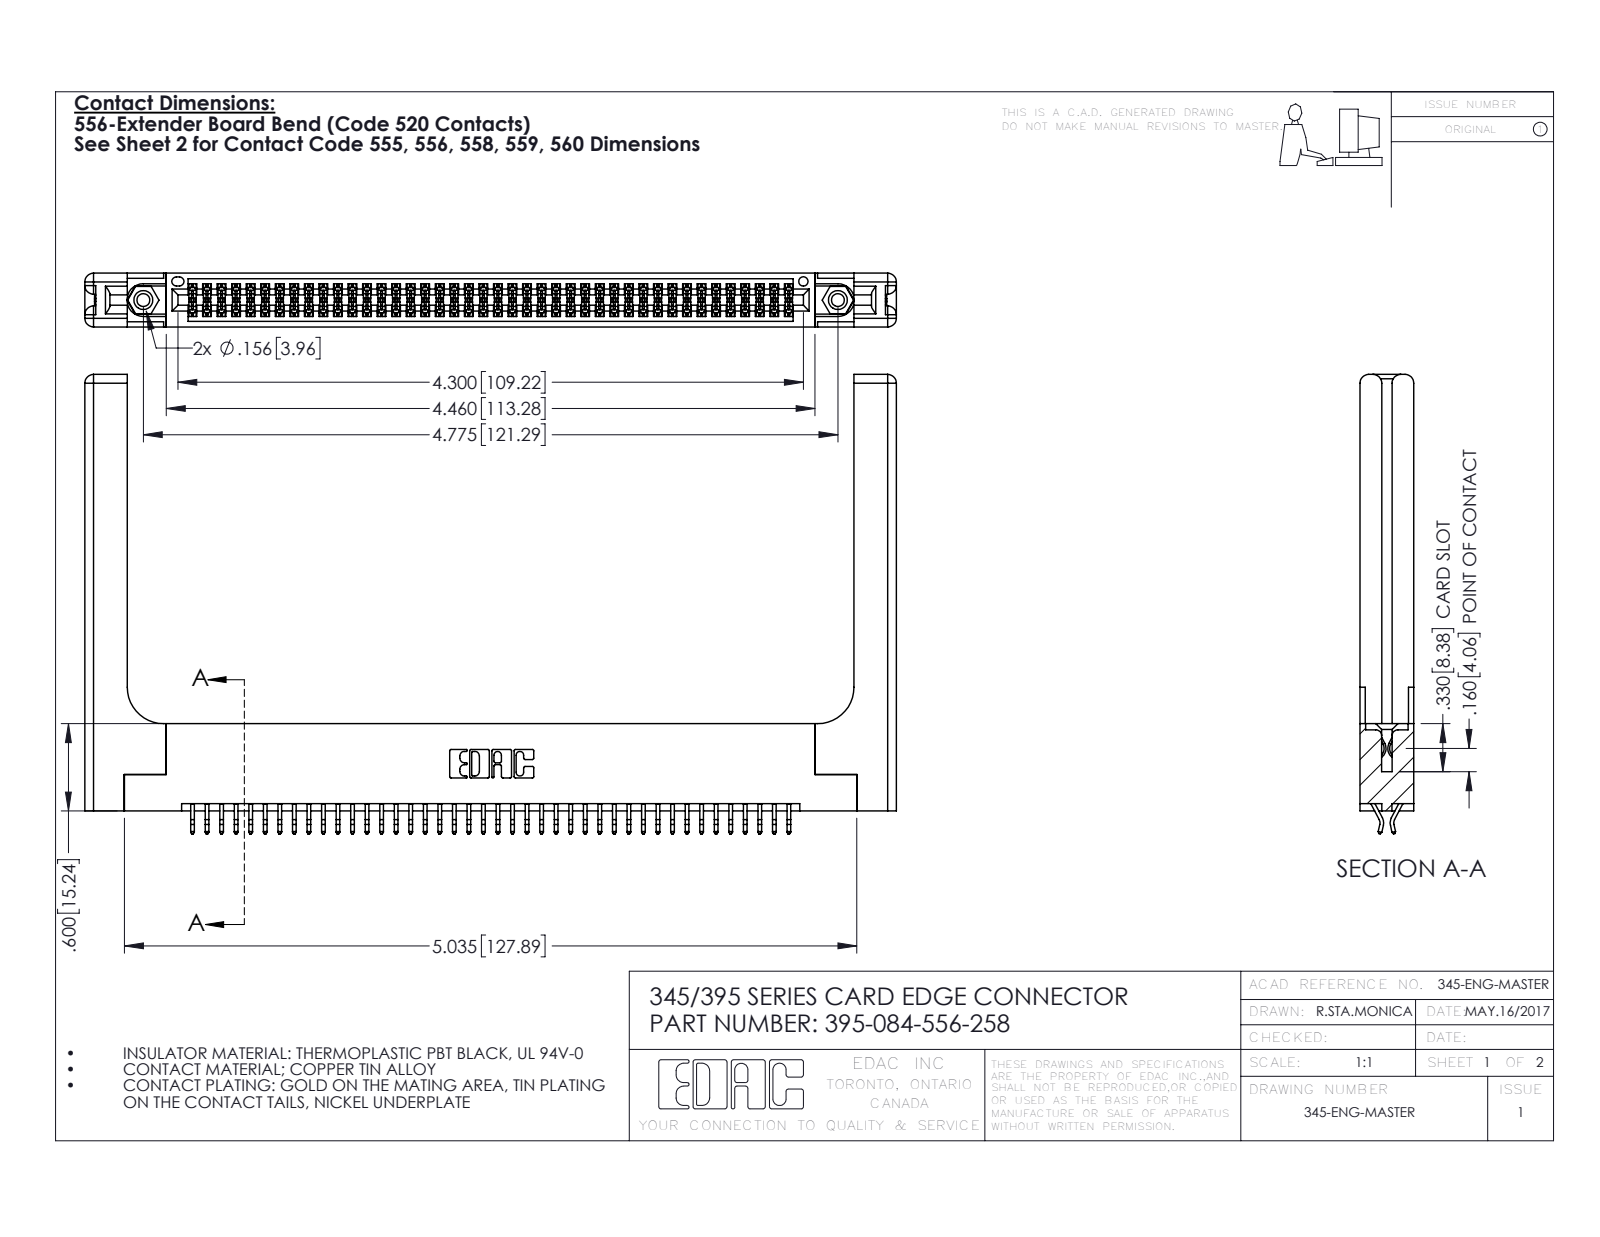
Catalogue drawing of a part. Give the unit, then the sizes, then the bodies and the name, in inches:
Units: inches
Overall size (bounding box): 5.579 × 3.157 × 0.37
Round holes (diameter × count): ⌀0.089 ×2, ⌀0.125 ×2, ⌀0.156 ×2, ⌀0.064 ×1
Round bosses / shafts (diameter × count): ⌀0.155 ×2
Partial cylindrical surfaces — rounded edges, fillets, slot ends (radius × count): R0.006 ×126, R0.01 ×22, R0.06 ×16, R0.007 ×6, R0.031 ×6, R0.026 ×3, R0.01 ×2, R0.014 ×2
Main face-to-face distances: 0.072, 0.37, 0.298, 0.2, 0.025, 0.098, 0.272, 0.225, 0.148, 0.15
Hole centre spacings: 0.27, 4.539, 4.775
Volume: 1.357 in³ · Surface area: 39.26 in²
Bodies: 89 solids, 5086 faces (3336 planar, 1690 cylindrical, 60 other)
Part name (STEP PRODUCT): 345-292-001_556 Tail; 345-220-058_345-220-058; 395-084-556-258; 345-250-001_345-250-001-102 (+1 more)
STEP written by: SolidWorks 2016 (CONFIG_CONTROL_DESIGN)
